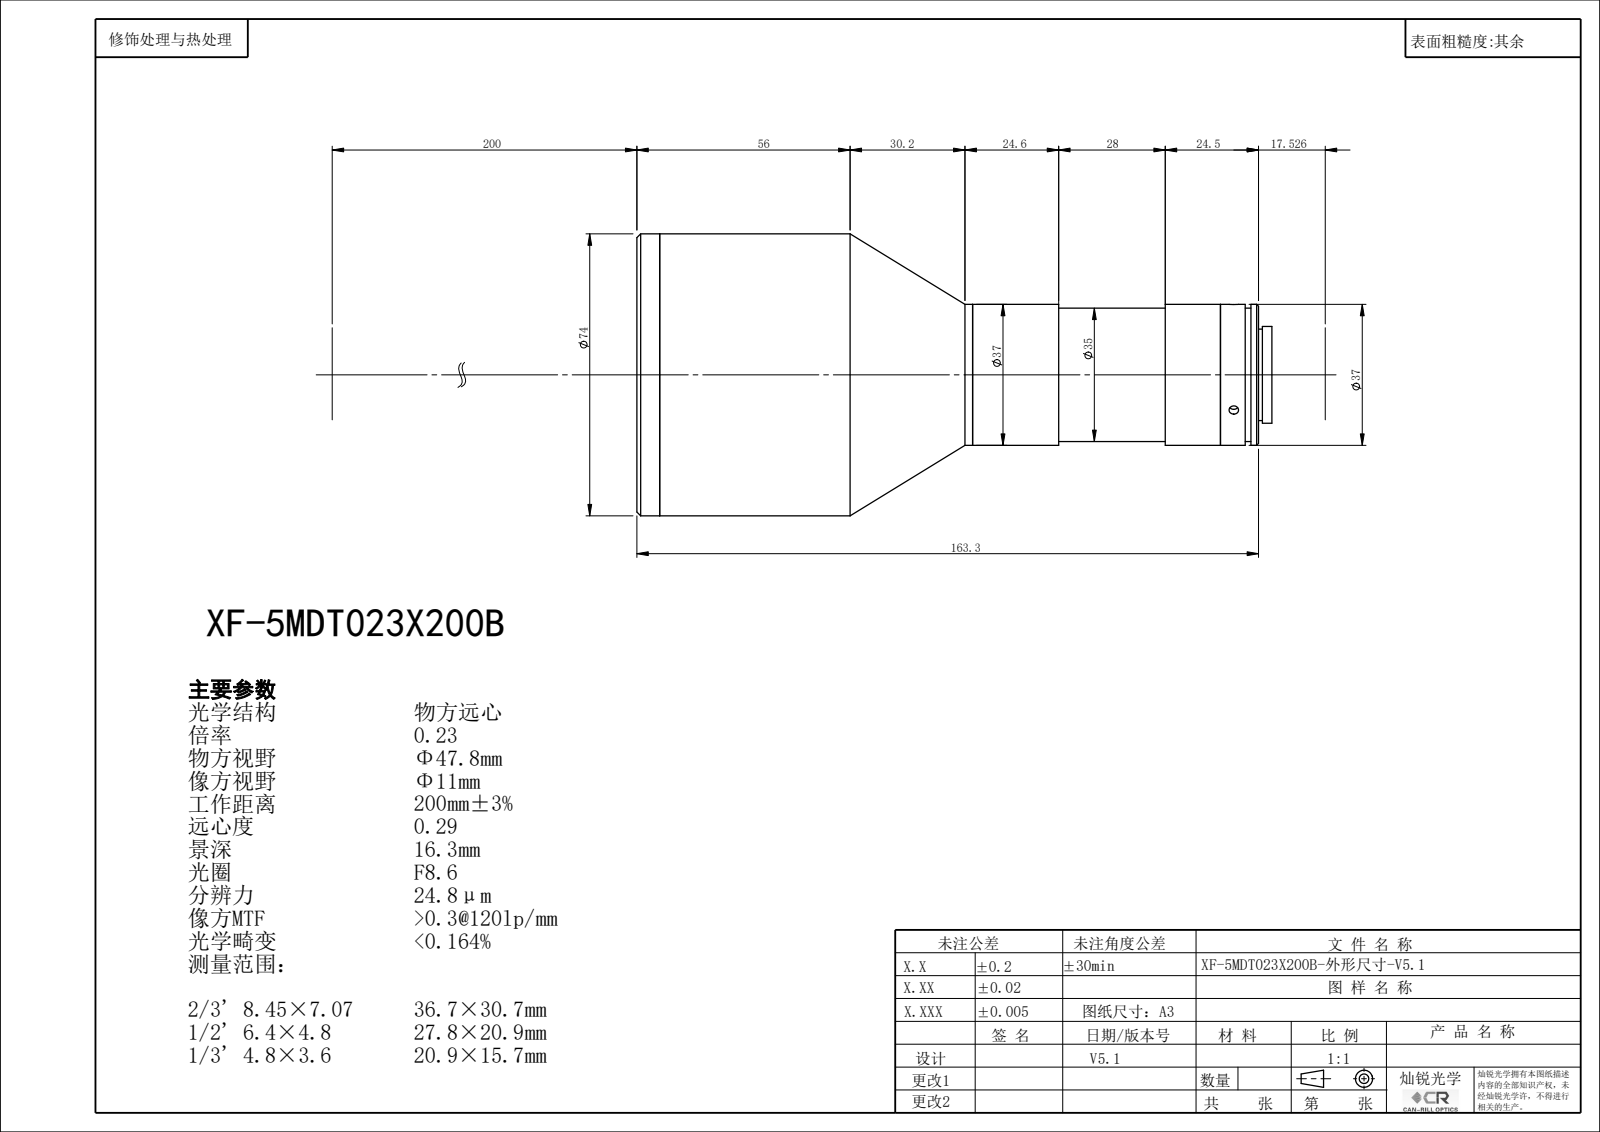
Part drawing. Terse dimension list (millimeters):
name: XF-5MDT023X200B-V5.1
written by: SolidWorks 2022 (CONFIG_CONTROL_DESIGN)
unit: mm
bodies: 0 solids, 76 faces (22 planar, 42 cylindrical, 12 other)
size: 166.76 × 74 × 74
holes: 3× ⌀2.5, 1× ⌀21.4, 1× ⌀23, 1× ⌀62, 1× ⌀67, 1× ⌀70
bosses: 1× ⌀74, 1× ⌀37, 1× ⌀35, 1× ⌀30, 1× ⌀25.4, 1× ⌀24
face distances: 2.43, 157.26, 159.69, 163.26, 6, 3.57, 10, 147.26, 149.69, 153.26
